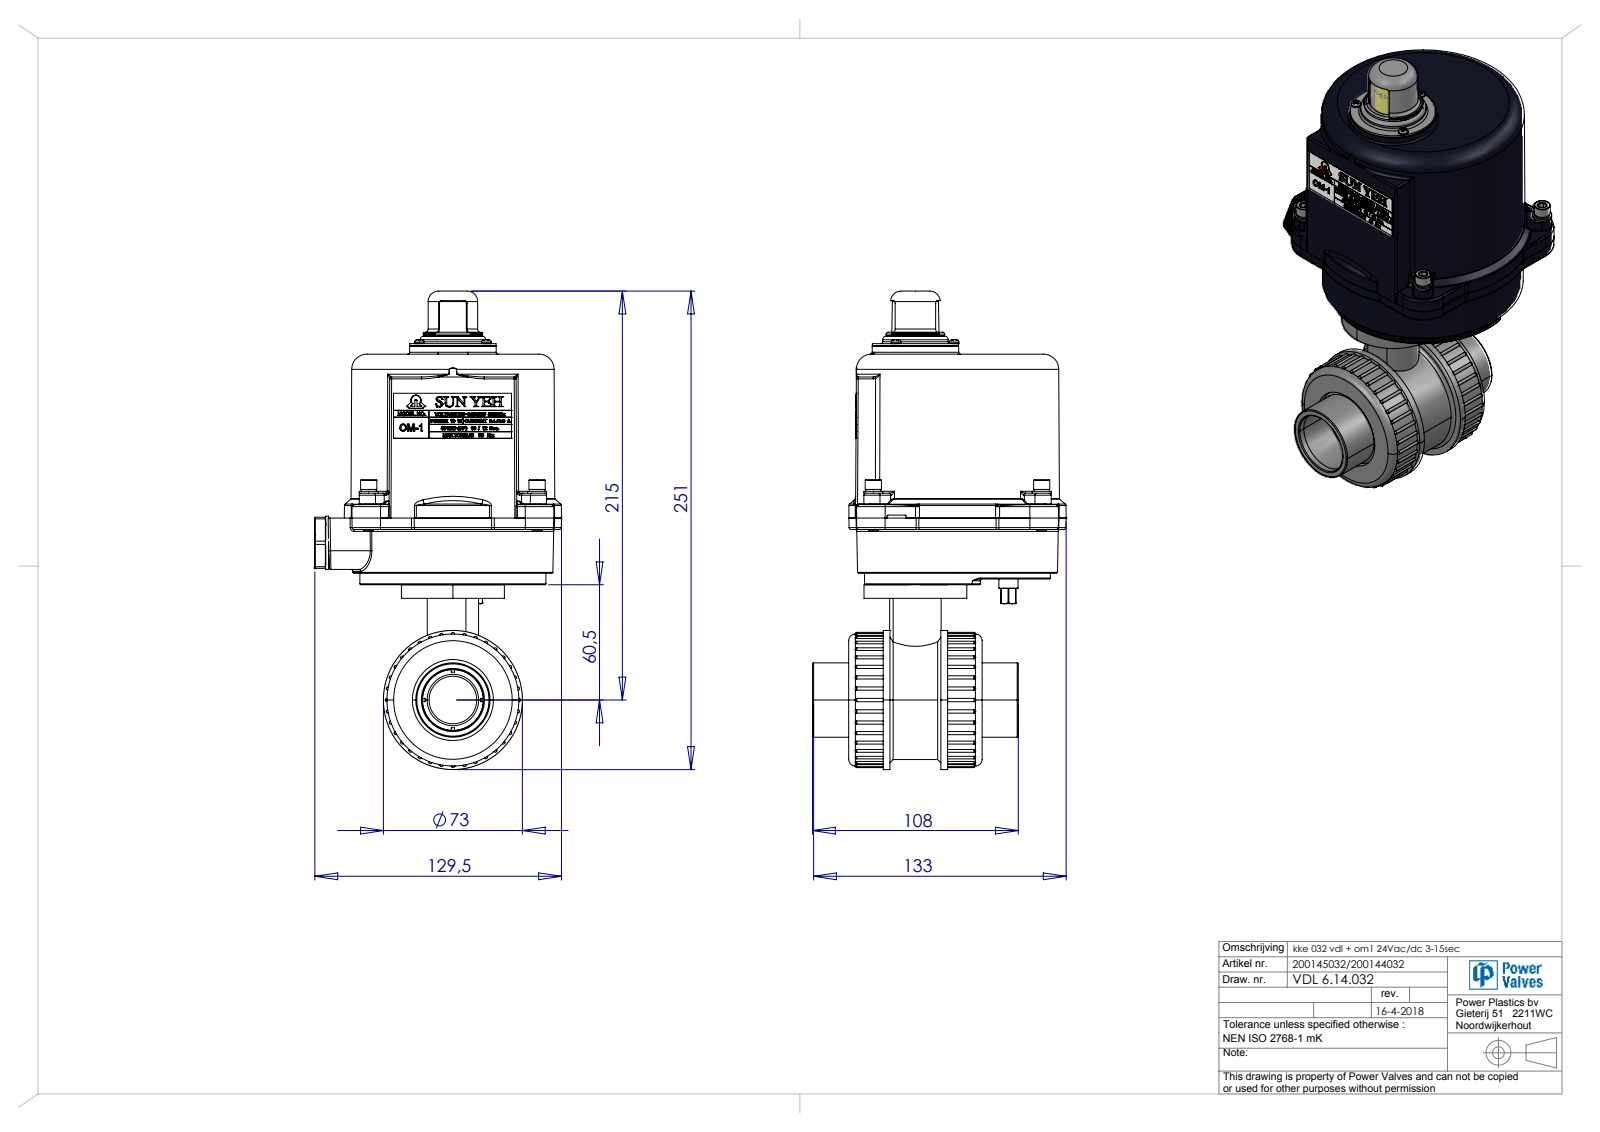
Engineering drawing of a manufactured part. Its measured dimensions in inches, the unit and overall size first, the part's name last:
Units: inches
Overall size (bounding box): 9.886 × 5.24 × 5.097
Round holes (diameter × count): ⌀0.197 ×8, ⌀0.128 ×4, ⌀0.163 ×4, ⌀0.165 ×4, ⌀0.181 ×4, ⌀0.217 ×4, ⌀0.138 ×3, ⌀0.097 ×2, ⌀0.097 ×2, ⌀0.114 ×2, ⌀0.268 ×2, ⌀0.315 ×2
Round bosses / shafts (diameter × count): ⌀0.197 ×8, ⌀0.394 ×5, ⌀0.315 ×5, ⌀0.335 ×4, ⌀0.173 ×4, ⌀1.102 ×3, ⌀0.118 ×3, ⌀0.827 ×2
Partial cylindrical surfaces — rounded edges, fillets, slot ends (radius × count): R0.039 ×65, R0.035 ×40, R0.009 ×28, R0.122 ×28, R0.059 ×17, R0.02 ×14, R0.004 ×10, R0.053 ×8
Main face-to-face distances: 3.287, 1.378, 4.665, 4.764, 0.098, 3.386, 0.276, 0.118, 0.236, 4.547
Hole centre spacings: 0.984, 0.708, 2.048, 3.48, 0.118, 0.157, 0.276, 0.709
Volume: 33.26 in³ · Surface area: 347.8 in²
Bodies: 22 solids, 4362 faces (1633 planar, 940 cylindrical, 1789 other)
Part name (STEP PRODUCT): OM1 (dimension); VDL 6.14.032; OMA150A (本體座-PS); OM1比例式貼紙 (+6 more)
STEP written by: SolidWorks 2014 (AUTOMOTIVE_DESIGN)
